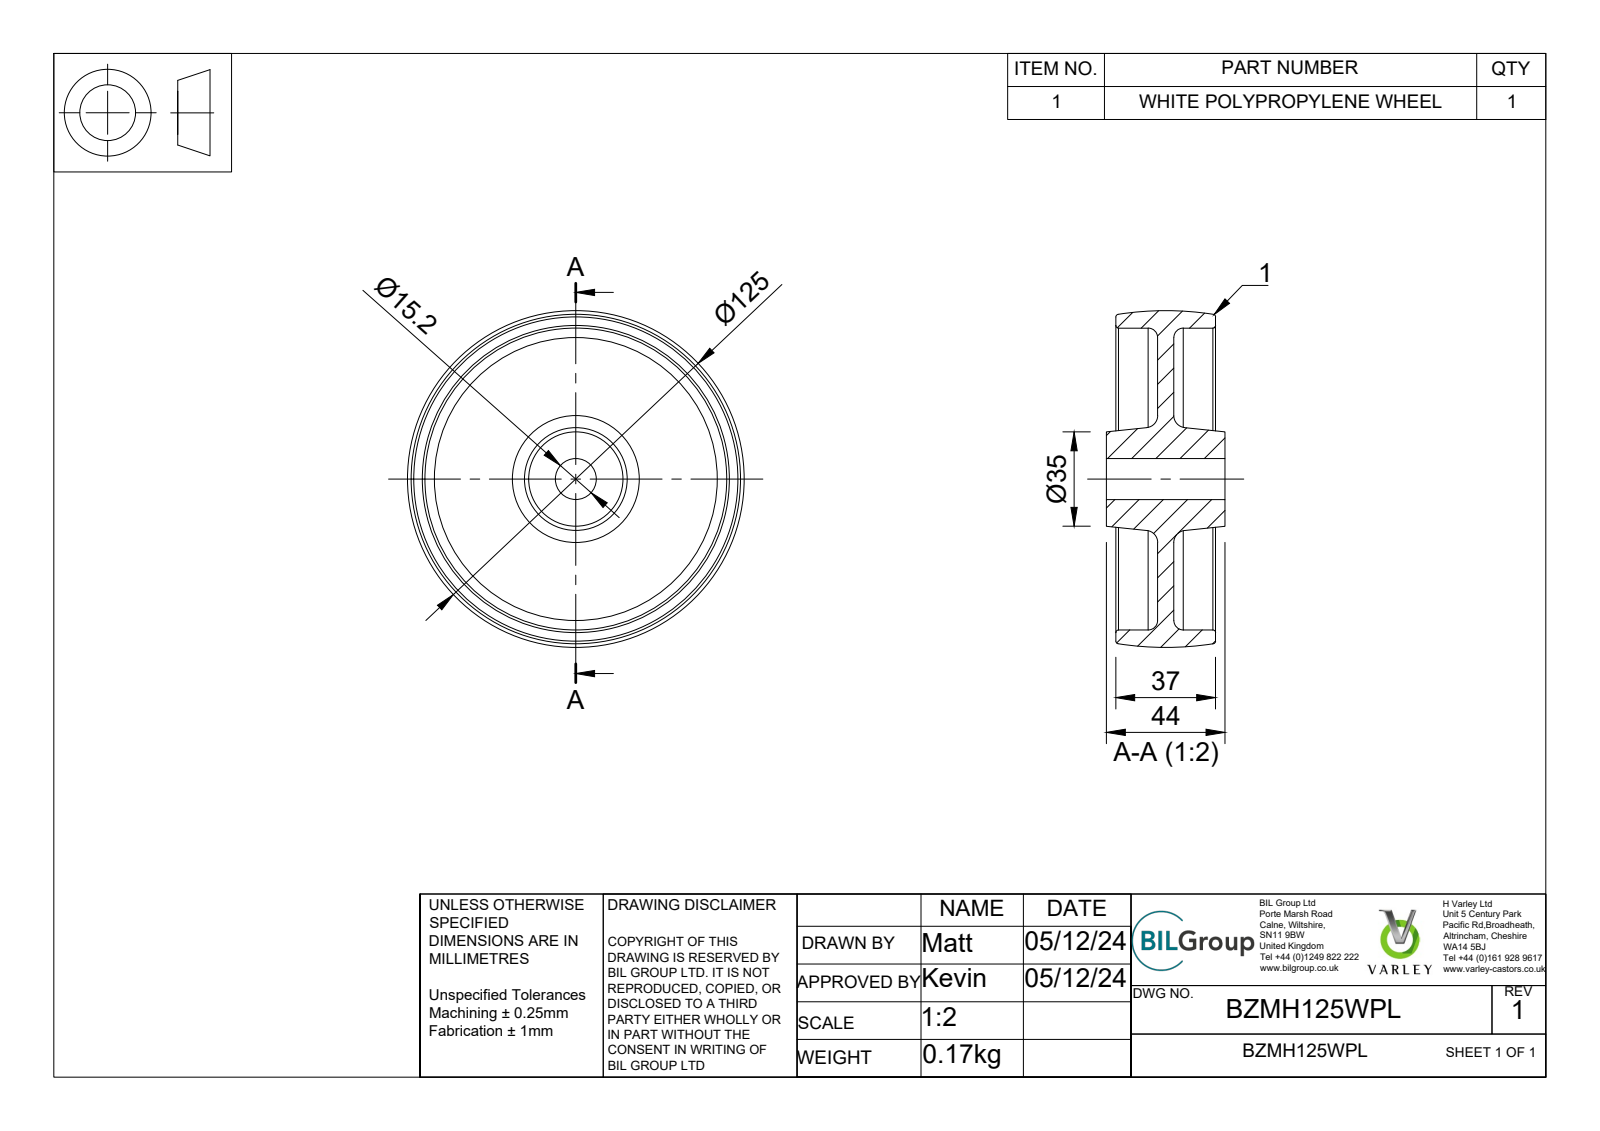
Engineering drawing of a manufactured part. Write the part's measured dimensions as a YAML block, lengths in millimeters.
part_name: "BZMH125WPL v2; BZMH125WPL"
step_written_by: "Autodesk Translation Framework v13.20.0.188 (AP242_MANAGED_MODEL_BASED_3D_ENGINEERING_MIM_LF)"
units: millimeters
bodies: {solids: 1, faces: 20, planar: 6, cylindrical: 3, other: 11}
overall_size: [125, 125, 44]
volume: 176661
surface_area: 52527
round_holes:
  - {diameter: 15.2, count: 1}
  - {diameter: 112, count: 1}
face_to_face_distances: [6, 15.5, 21.5, 3.5, 19, 25, 40.5, 37, 44]
